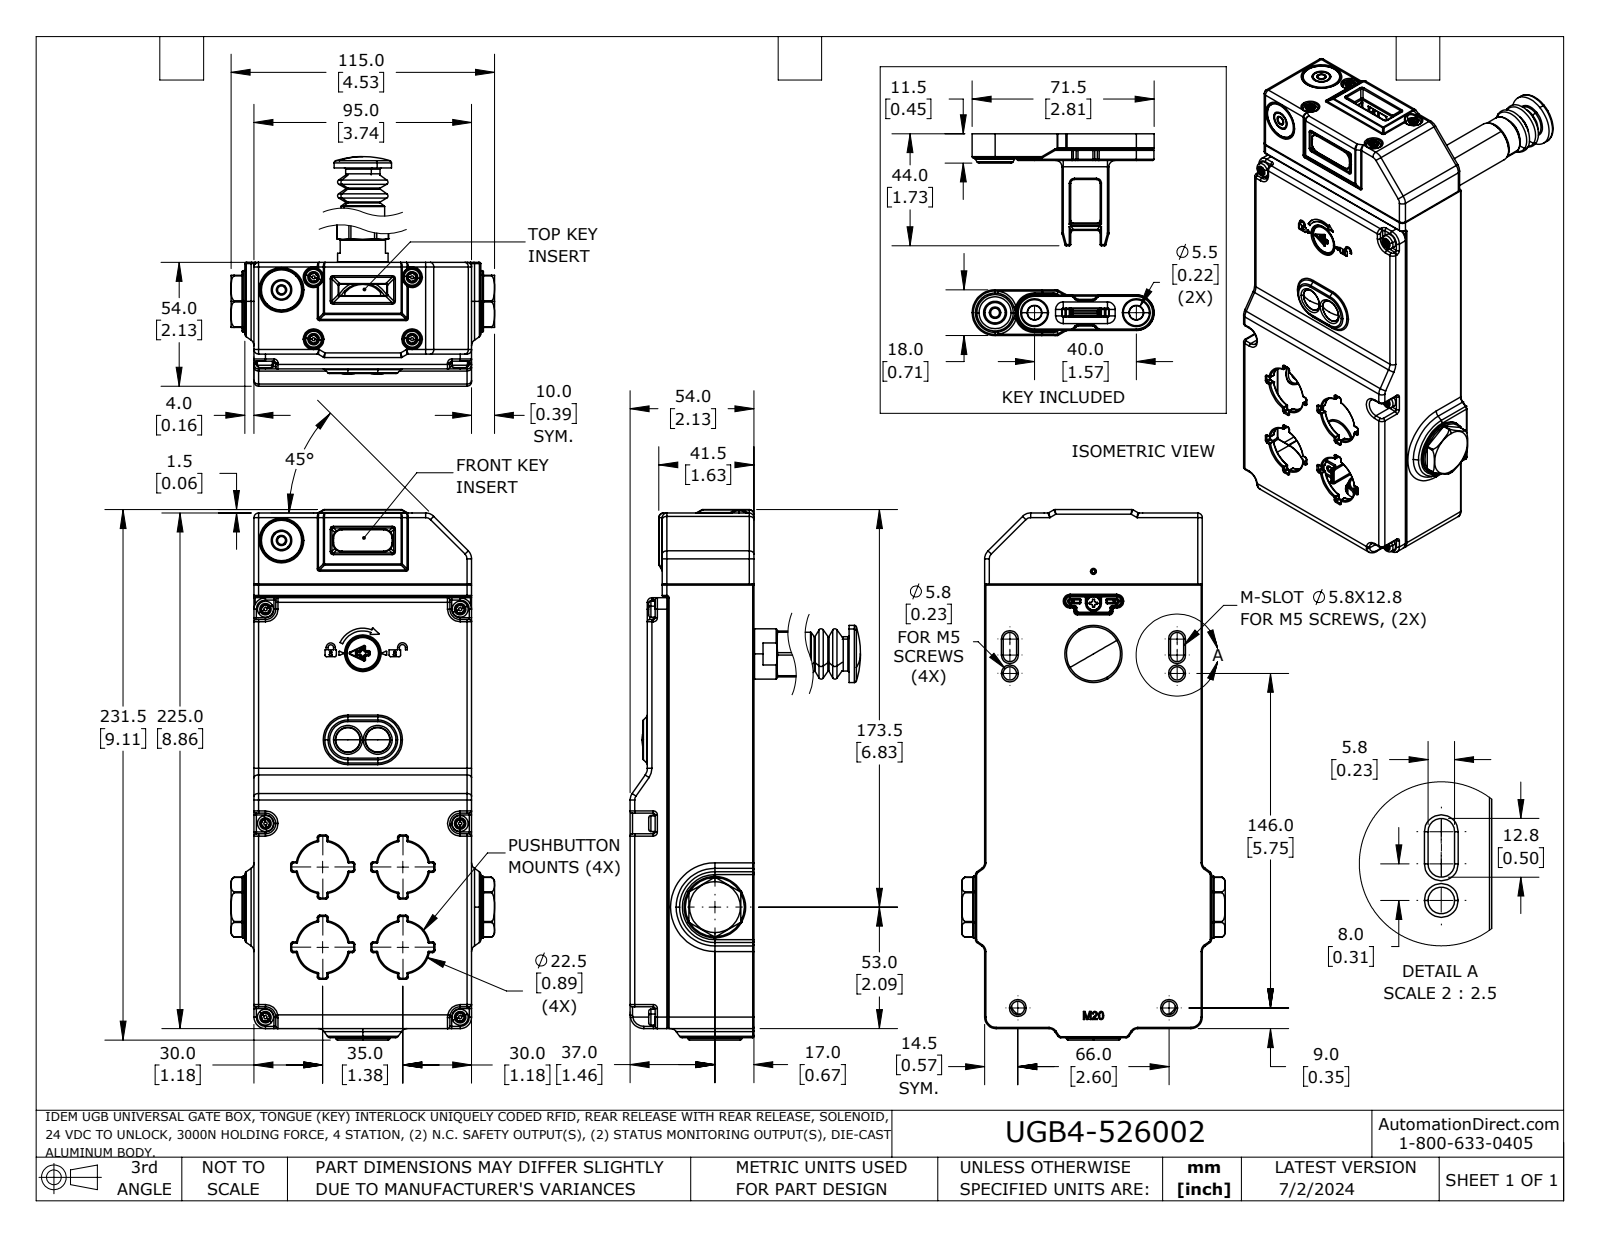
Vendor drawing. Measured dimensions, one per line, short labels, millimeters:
name: 526002 UGB4-KLTM-RFID-RR Manual Override
written by: SolidWorks 2021 (CONFIG_CONTROL_DESIGN)
unit: mm
bodies: 34 solids, 5492 faces (1266 planar, 2197 cylindrical, 2029 other)
size: 244 × 153.6 × 115
volume: 334 580 mm³; area: 212 016 mm²
holes: 10× ⌀3.3, 10× ⌀4, 8× ⌀2.5, 8× ⌀4.5, 8× ⌀8, 5× ⌀5, 5× ⌀12, 4× ⌀4.2, 4× ⌀5.5, 4× ⌀5.8, 4× ⌀9, 3× ⌀14
bosses: 12× ⌀3.5, 10× ⌀7, 6× ⌀6.2, 6× ⌀1.4, 5× ⌀6, 4× ⌀1.3, 3× ⌀16, 2× ⌀18.2
rounds: 670× R0.5, 209× R1, 134× R0.3, 59× R0.2, 36× R2, 22× R0.4, 16× R0.8, 16× R1.5
face distances: 3, 2.2, 92, 7.5, 95, 51, 54, 51.8, 4.5, 46.5
hole spacings: 25.39, 15.5, 36.39, 41.86, 85, 2.83, 4.75, 5.7
